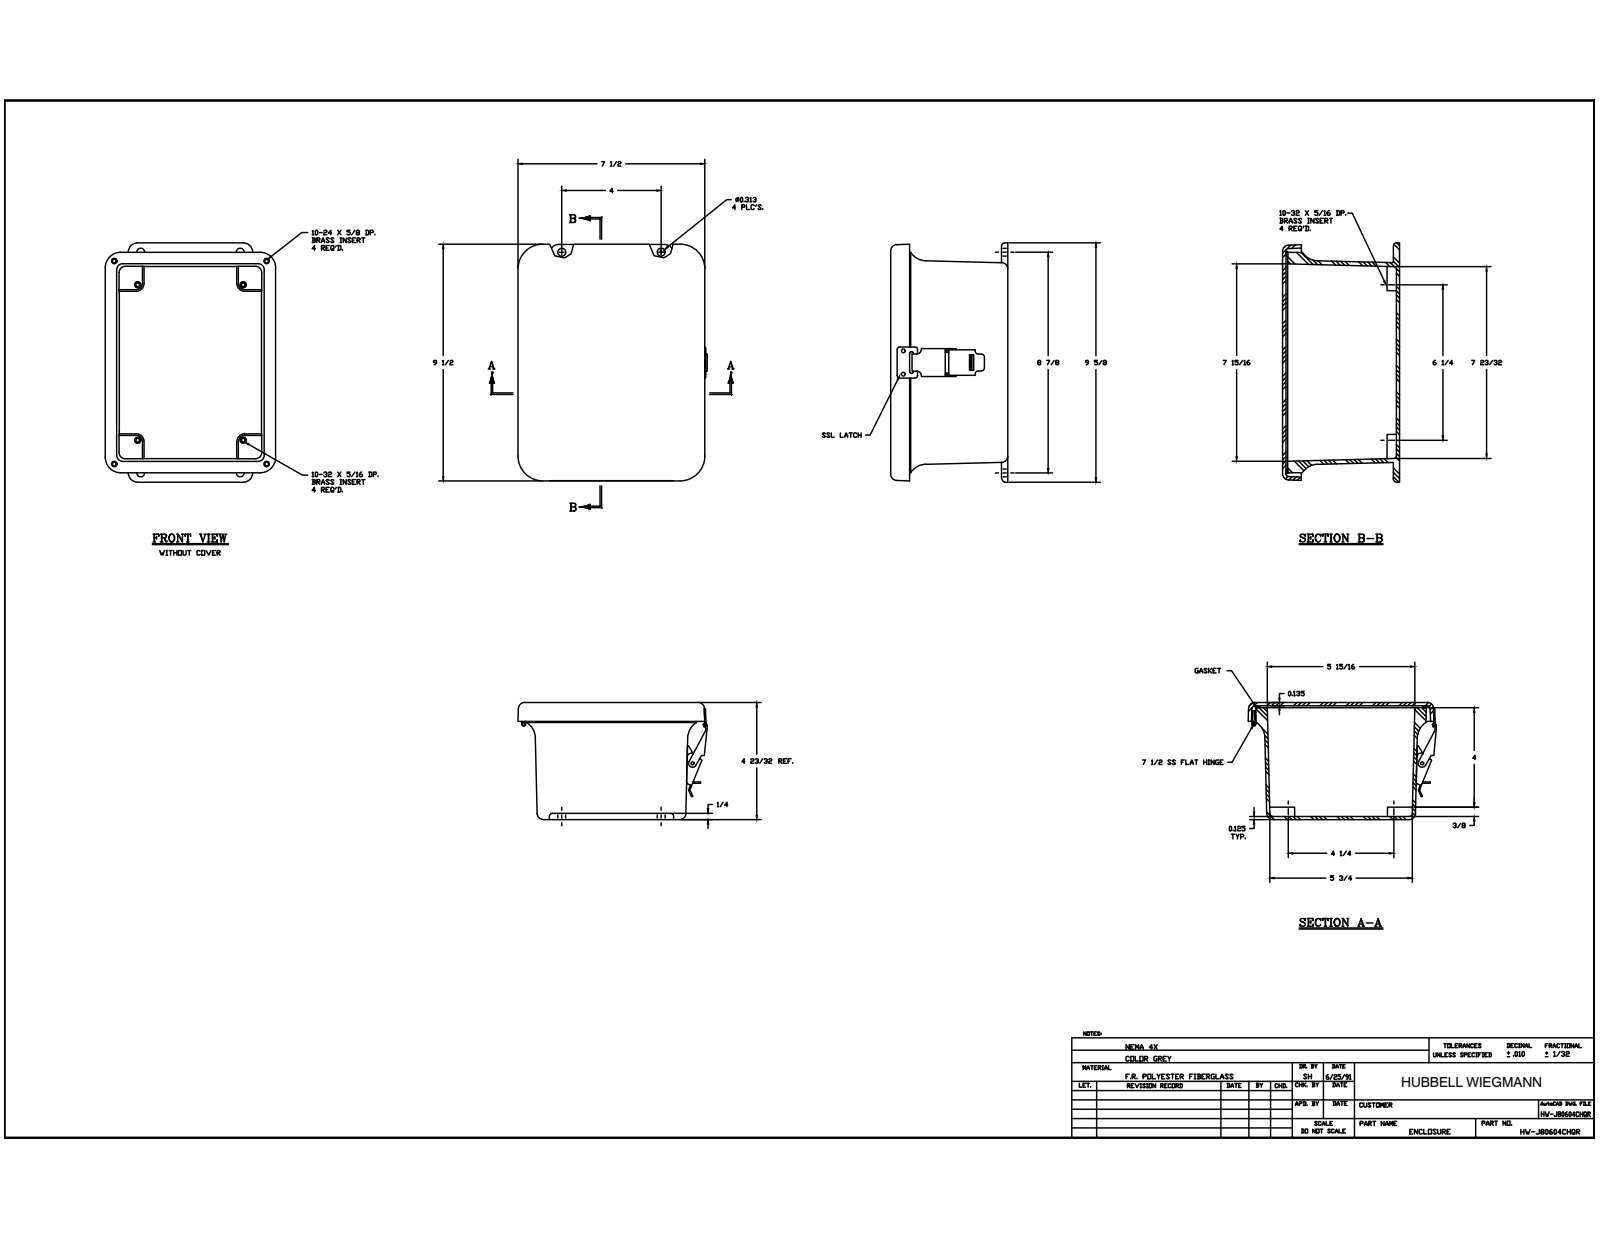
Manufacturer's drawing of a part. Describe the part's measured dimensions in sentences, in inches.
The part is named "J806HL_4; RMINS45821P_243; RMINS45821P_244; RMINS45821P_245 (+8 more)". Its 3-D file was written by "Autodesk Inventor 2014 (AUTOMOTIVE_DESIGN)". It is 26 solids with 676 faces: 277 planar, 274 cylindrical and 125 other. Overall it measures 9.625 by 7.605 by 4.715 inches. Its volume is 45.41 cubic inches and its surface area 618.6 square inches. Round holes: 12 of diameter 0.14, 6 of diameter 0.131, 5 of diameter 0.152, 4 of diameter 0.104, 4 of diameter 0.156, 4 of diameter 0.218, 2 of diameter 0.13, 2 of diameter 0.135, 1 of diameter 0.085, 1 of diameter 0.375. Round bosses or shafts: 10 of diameter 0.125, 6 of diameter 0.25, 4 of diameter 0.27, 1 of diameter 0.3, 1 of diameter 0.17, 1 of diameter 0.155, 1 of diameter 0.12. Partial cylindrical surfaces (rounded edges, fillets, slot ends): 20 of radius 0.031, 16 of radius 0.125, 12 of radius 0.015, 8 of radius 0.045, 8 of radius 0.25, 6 of radius 0.03, 5 of radius 0.022, 4 of radius 0.06. The main face-to-face distances are 0.125, 0.135, 4.58, 4.715, 0.125, 4.455, 4.59, 4.5, 4.375, 0.08. The hole center spacings are 3.5, 0.75, 0.25, 0.937, 1.326, 5.271, 7.249, 8.864.
